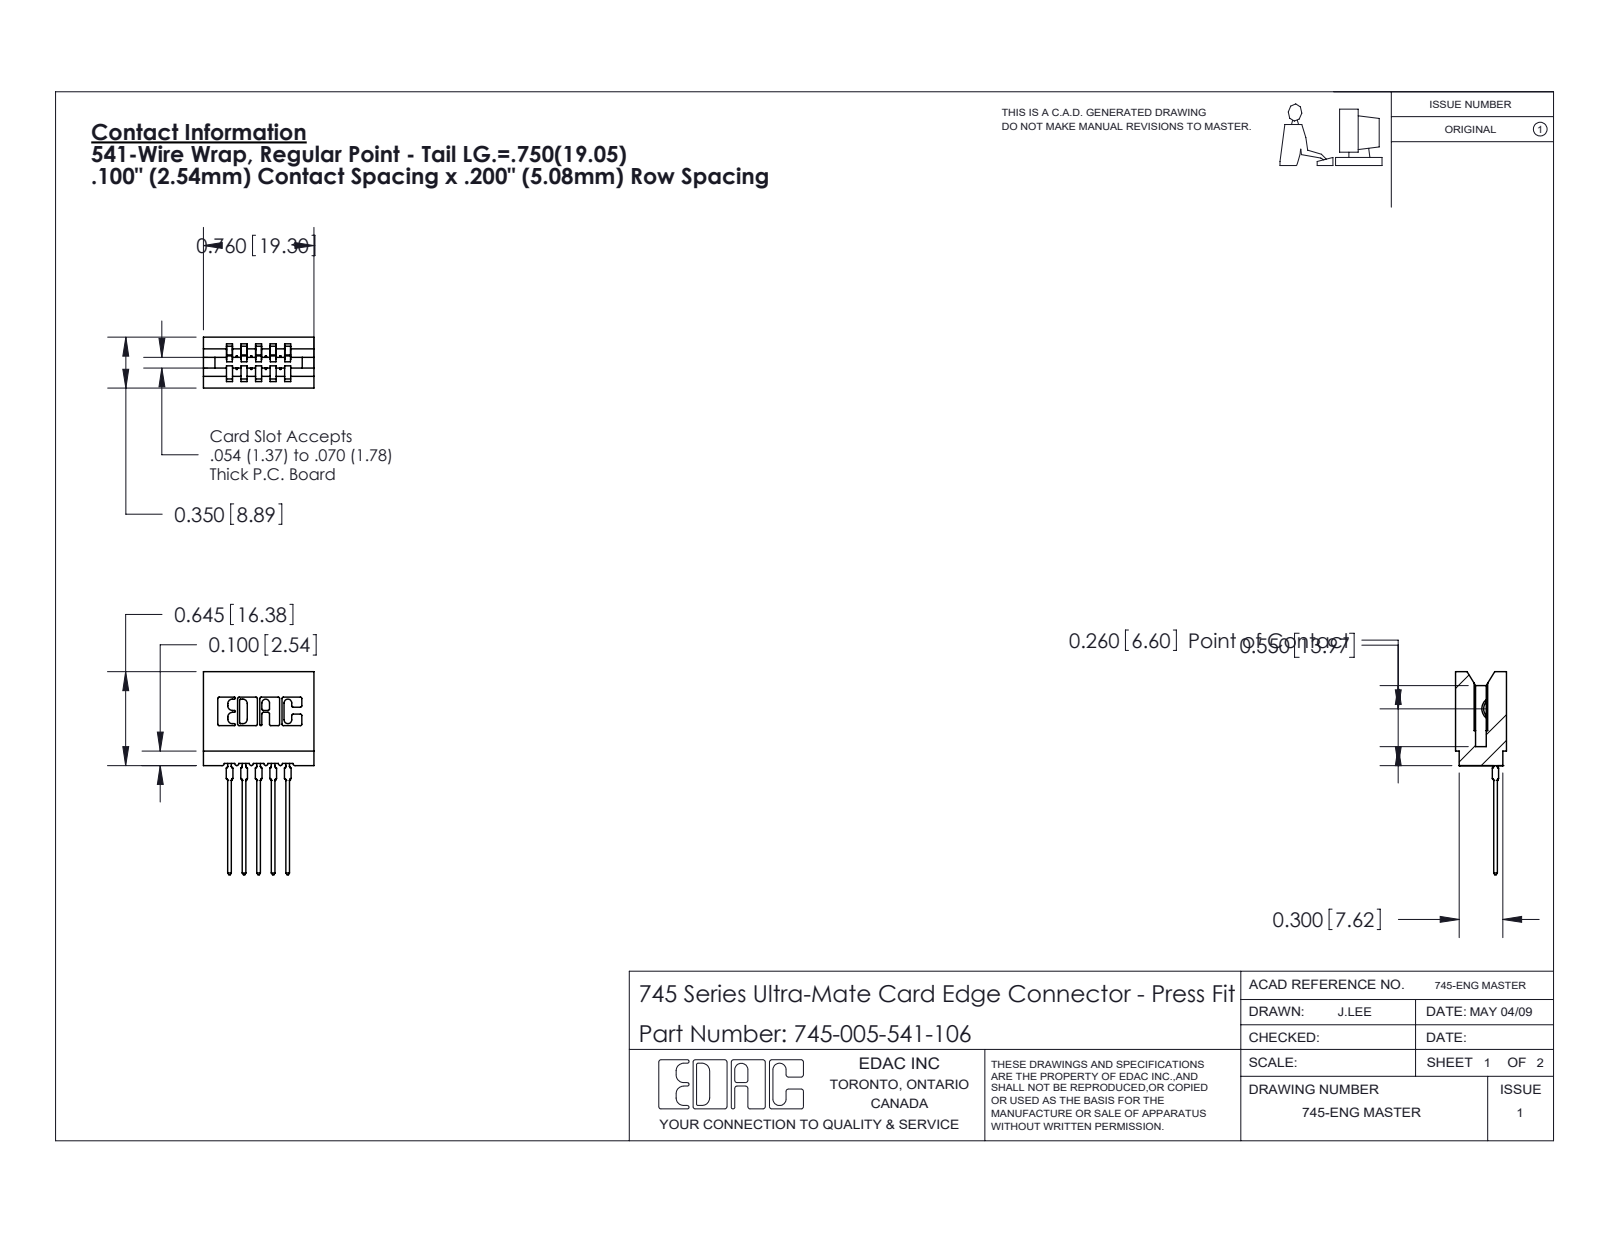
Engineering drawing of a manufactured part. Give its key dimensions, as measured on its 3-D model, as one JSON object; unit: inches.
{"part_name": "745-292-001_541; 745-005-541-106; 745 Part_Insulator Option - 06", "step_written_by": "SolidWorks 2020 (CONFIG_CONTROL_DESIGN)", "units": "inches", "bodies": {"solids": 6, "faces": 656, "planar": 391, "cylindrical": 135, "other": 130}, "overall_size": [1.396, 0.76, 0.35], "volume_in3": 0.117, "surface_area_in2": 4.588, "partial_cylinders_radius": [[0.01, 22], [0.015, 10], [0.021, 10], [0.007, 6], [0.031, 6], [0.005, 4], [0.011, 4], [0.026, 3]], "face_to_face_distances": [0.1, 0.2, 0.042, 0.3, 0.142, 0.058, 0.35, 0.158, 0.242, 0.138]}
